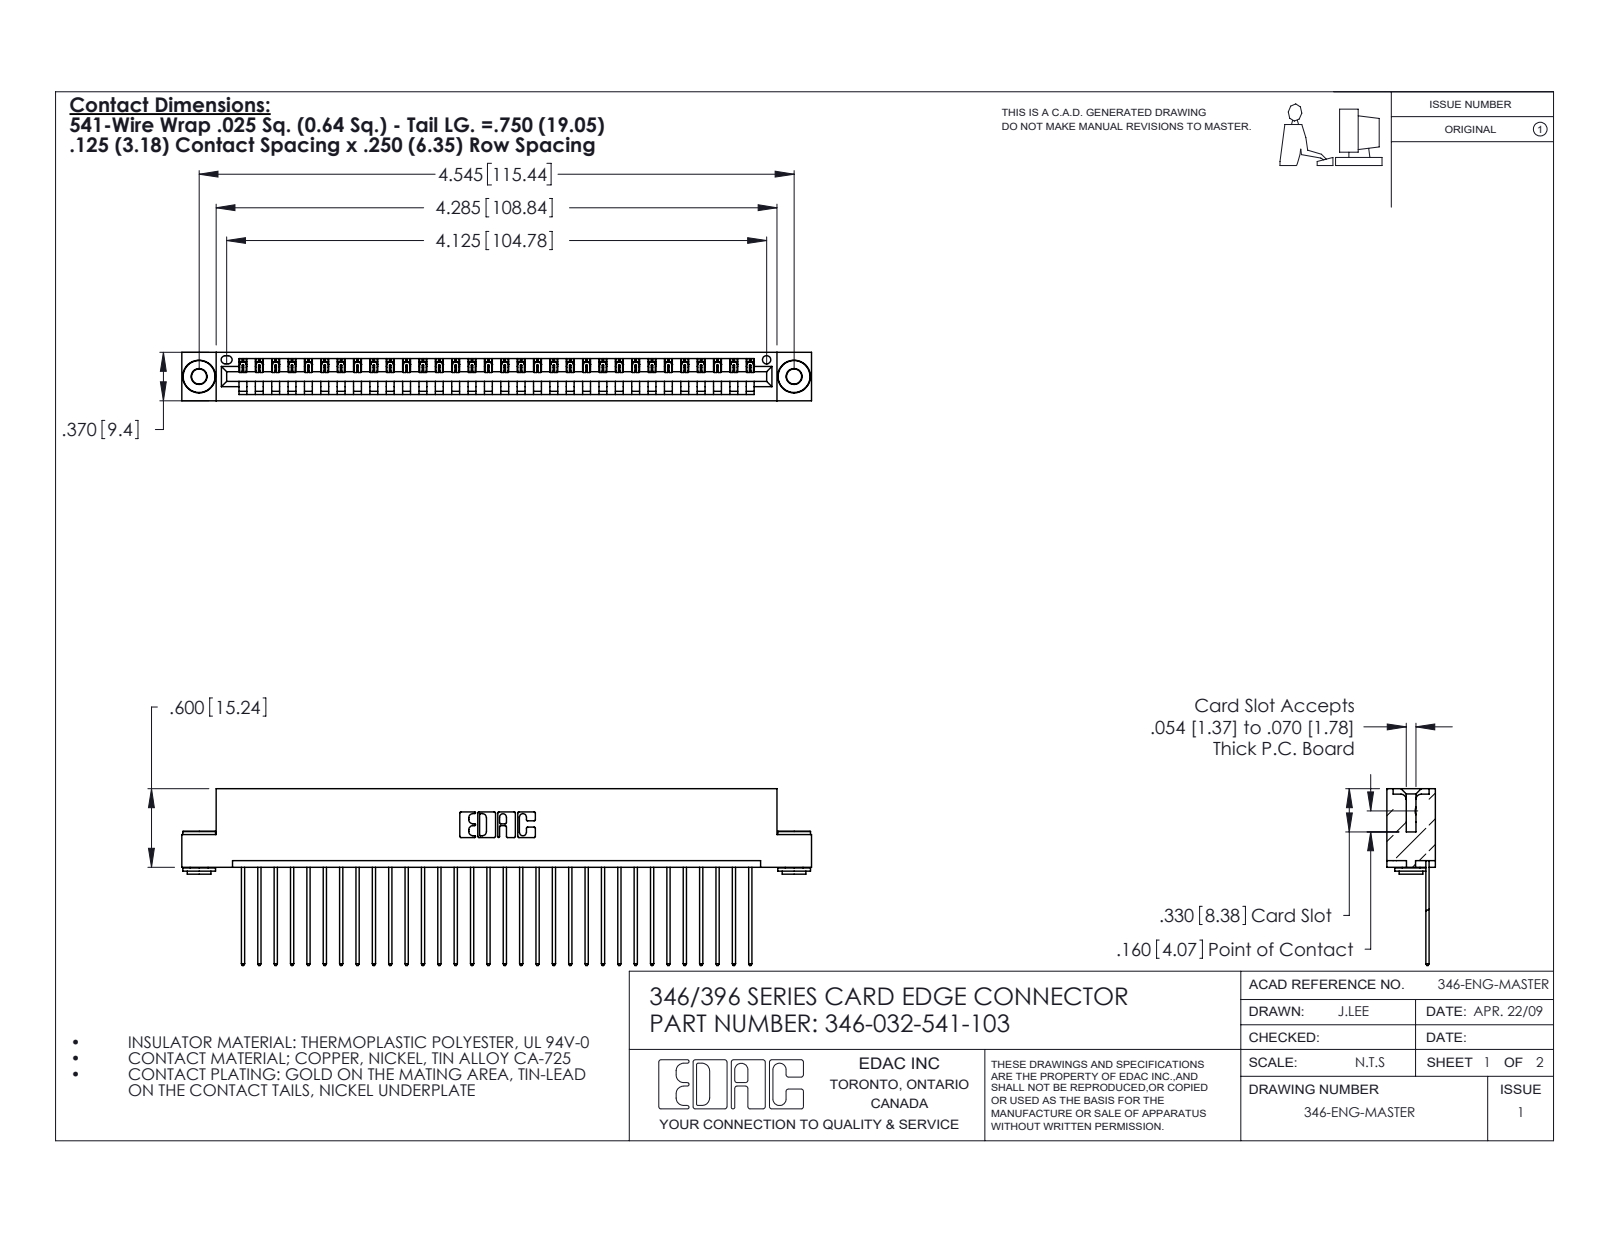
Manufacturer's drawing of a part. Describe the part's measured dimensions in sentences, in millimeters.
The part is named "345-250-002_345-250-002-102; 345-292-001_345-293-141; 346-032-541-103; 346 Part_Flush Mounting Lugs - 0.156 Dia-TH". Its 3-D file was written by "SolidWorks 2020 (CONFIG_CONTROL_DESIGN)". It is 35 solids with 2030 faces: 1380 planar, 642 cylindrical and 8 other. Overall it measures 122.2 by 34.3 by 9.4 millimeters. Its volume is 11 700 cubic millimeters and its surface area 15 440 square millimeters. Round holes: 2 of diameter 2.9, 2 of diameter 4, 1 of diameter 1.6. Round bosses or shafts: 2 of diameter 6.4, 2 of diameter 4.6, 2 of diameter 3.5. Partial cylindrical surfaces (rounded edges, fillets, slot ends): 64 of radius 0.2, 64 of radius 0.3, 22 of radius 0.3, 6 of radius 0.2, 6 of radius 0.8, 3 of radius 0.7, 2 of radius 0.8, 2 of radius 1. The main face-to-face distances are 1.2, 8.2, 9.4, 6.4, 0.6, 1.8, 7.6, 3.8, 5.6, 2.5. The hole center spacings are 6.2, 110.2, 115.4.
